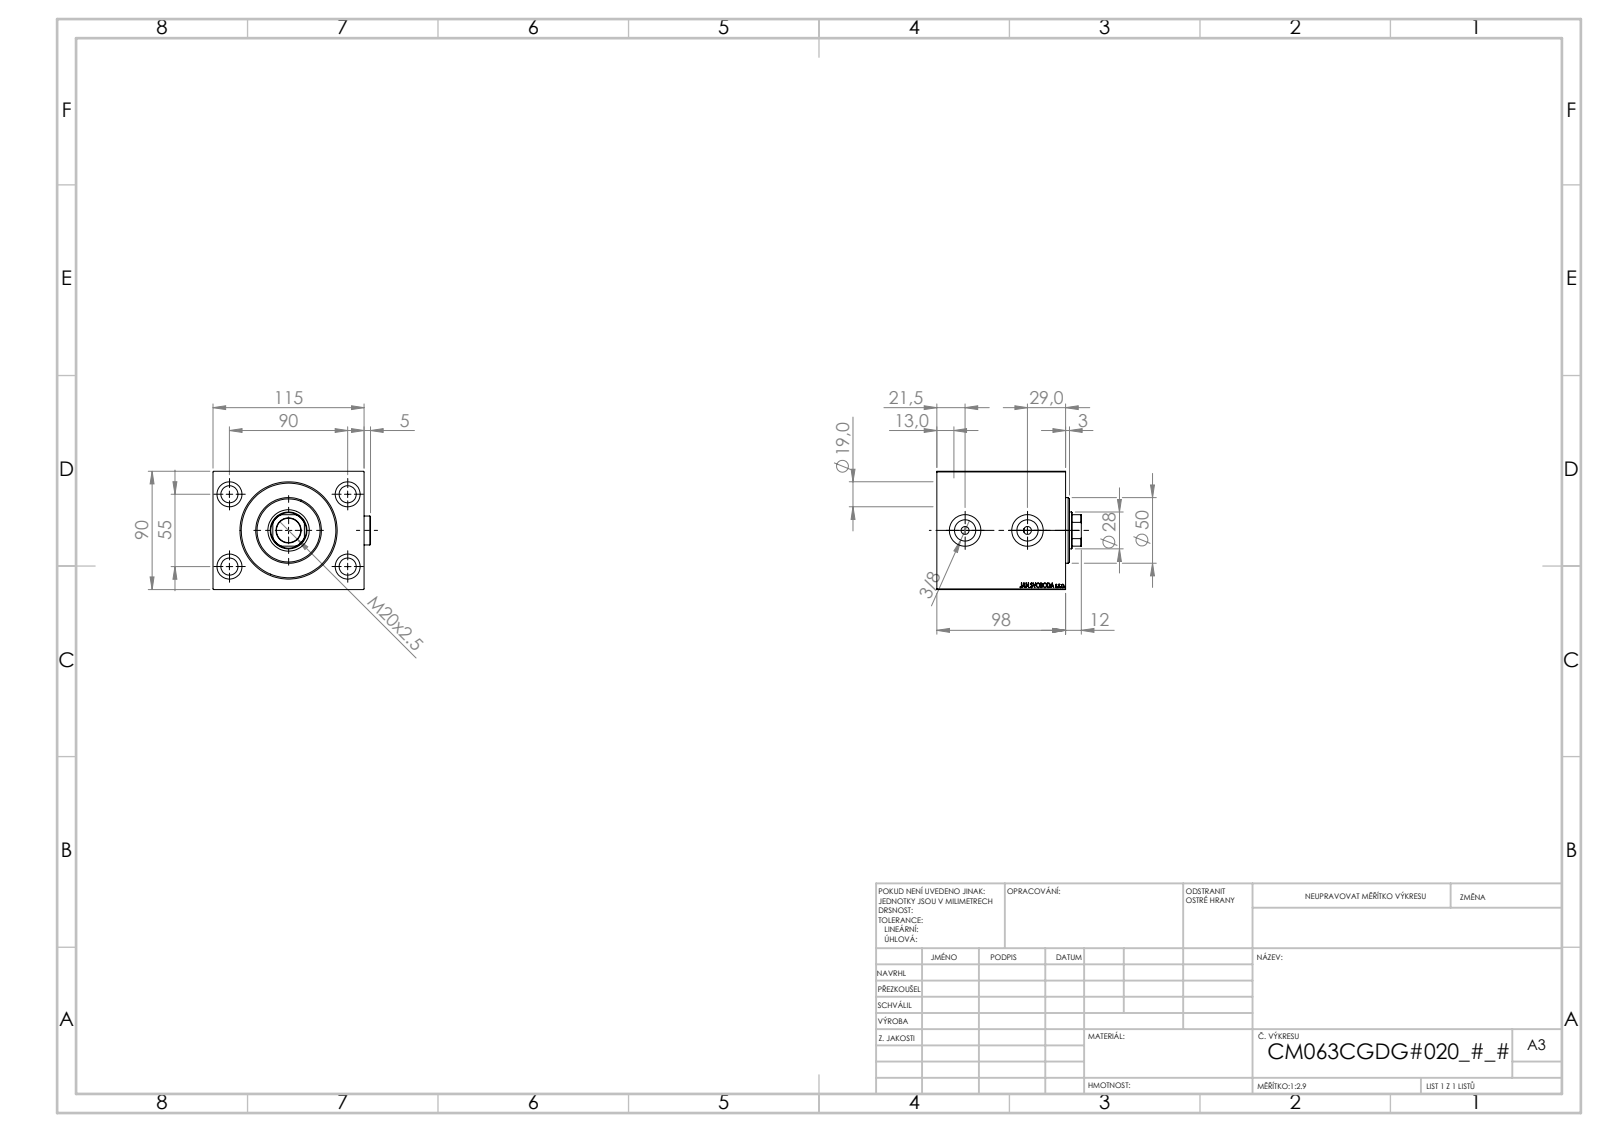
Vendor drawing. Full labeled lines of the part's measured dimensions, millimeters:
Part name (STEP PRODUCT): V450CM_VC_B; Zatka_OIL_PORT; V450CM_C_Body; V450CM_C_VCP
STEP written by: SolidWorks 2019 (CONFIG_CONTROL_DESIGN)
Units: millimetres
Bodies: 5 solids, 917 faces (443 planar, 76 cylindrical, 398 other)
Overall size (bounding box): 119.9 × 110 × 90
Volume: 913 985 mm³ · Surface area: 124 329 mm²
Round holes (diameter × count): ⌀13 ×4, ⌀19 ×4, ⌀6 ×2, ⌀16.17 ×2, ⌀24 ×2, ⌀18.5 ×1, ⌀28 ×1, ⌀31.5 ×1, ⌀63 ×1, ⌀65 ×1, ⌀72 ×1
Round bosses / shafts (diameter × count): ⌀22 ×2, ⌀50 ×1
Partial cylindrical surfaces — rounded edges, fillets, slot ends (radius × count): R13.5 ×1
Main face-to-face distances: 90, 115, 98, 51, 47, 21.6, 29.4, 76.4, 10, 31.6
Hole centre spacings: 52.74, 55, 90, 105.48, 47.5
